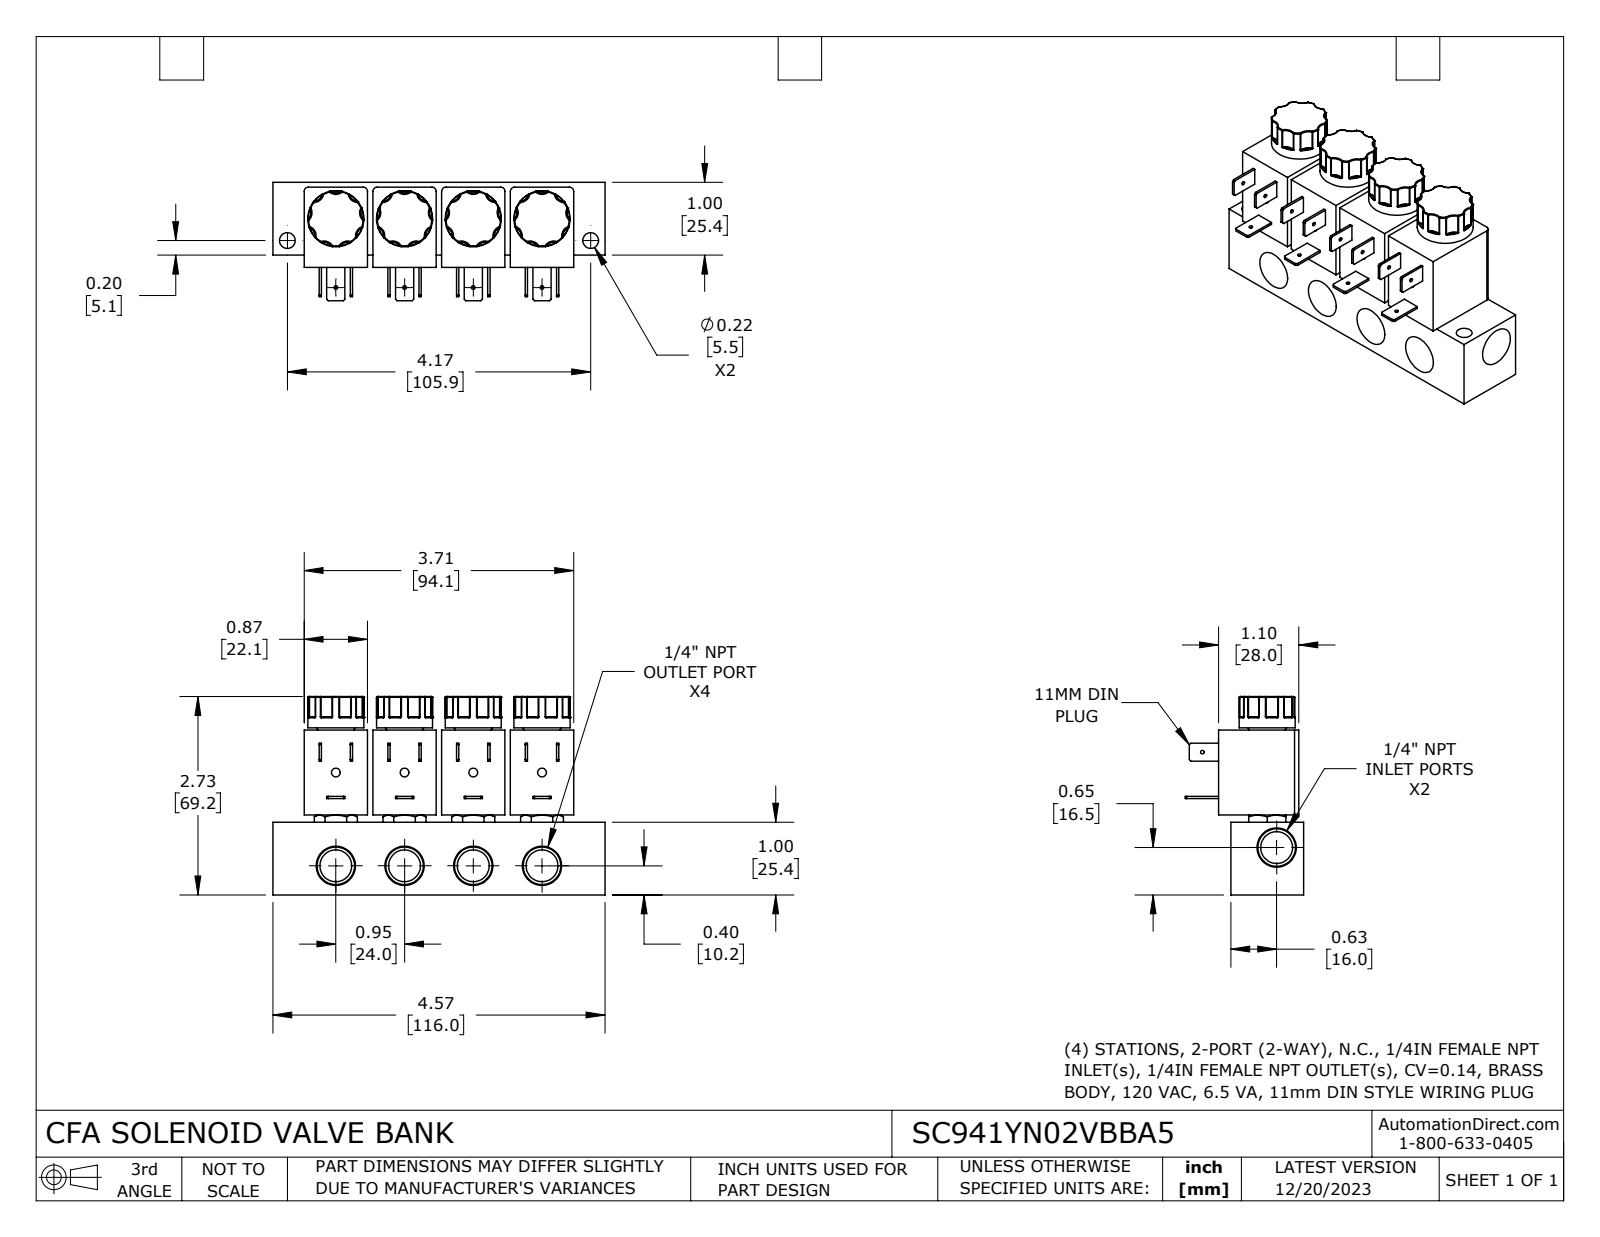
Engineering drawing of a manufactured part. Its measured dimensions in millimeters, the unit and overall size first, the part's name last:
Units: millimetres
Overall size (bounding box): 116 × 69.2 × 41.3
Round holes (diameter × count): ⌀1.3 ×5, ⌀11.1 ×5, ⌀3 ×4, ⌀5.5 ×2
Round bosses / shafts (diameter × count): ⌀19.6 ×4
Partial cylindrical surfaces — rounded edges, fillets, slot ends (radius × count): R0.3 ×72, R3.4 ×34, R1.5 ×8, R3.4 ×2
Main face-to-face distances: 25.4, 24, 29.7, 48, 46.1, 22.1, 4.3, 1.7, 23.7, 28
Hole centre spacings: 24, 32.6, 40.5, 24, 48, 48, 72, 40.5
Volume: 150 500 mm³ · Surface area: 39 390 mm²
Bodies: 1 solid, 868 faces (192 planar, 184 cylindrical, 492 other)
Part name (STEP PRODUCT): SC941YN02VBBA5
STEP written by: SolidWorks 2023 (CONFIG_CONTROL_DESIGN)
